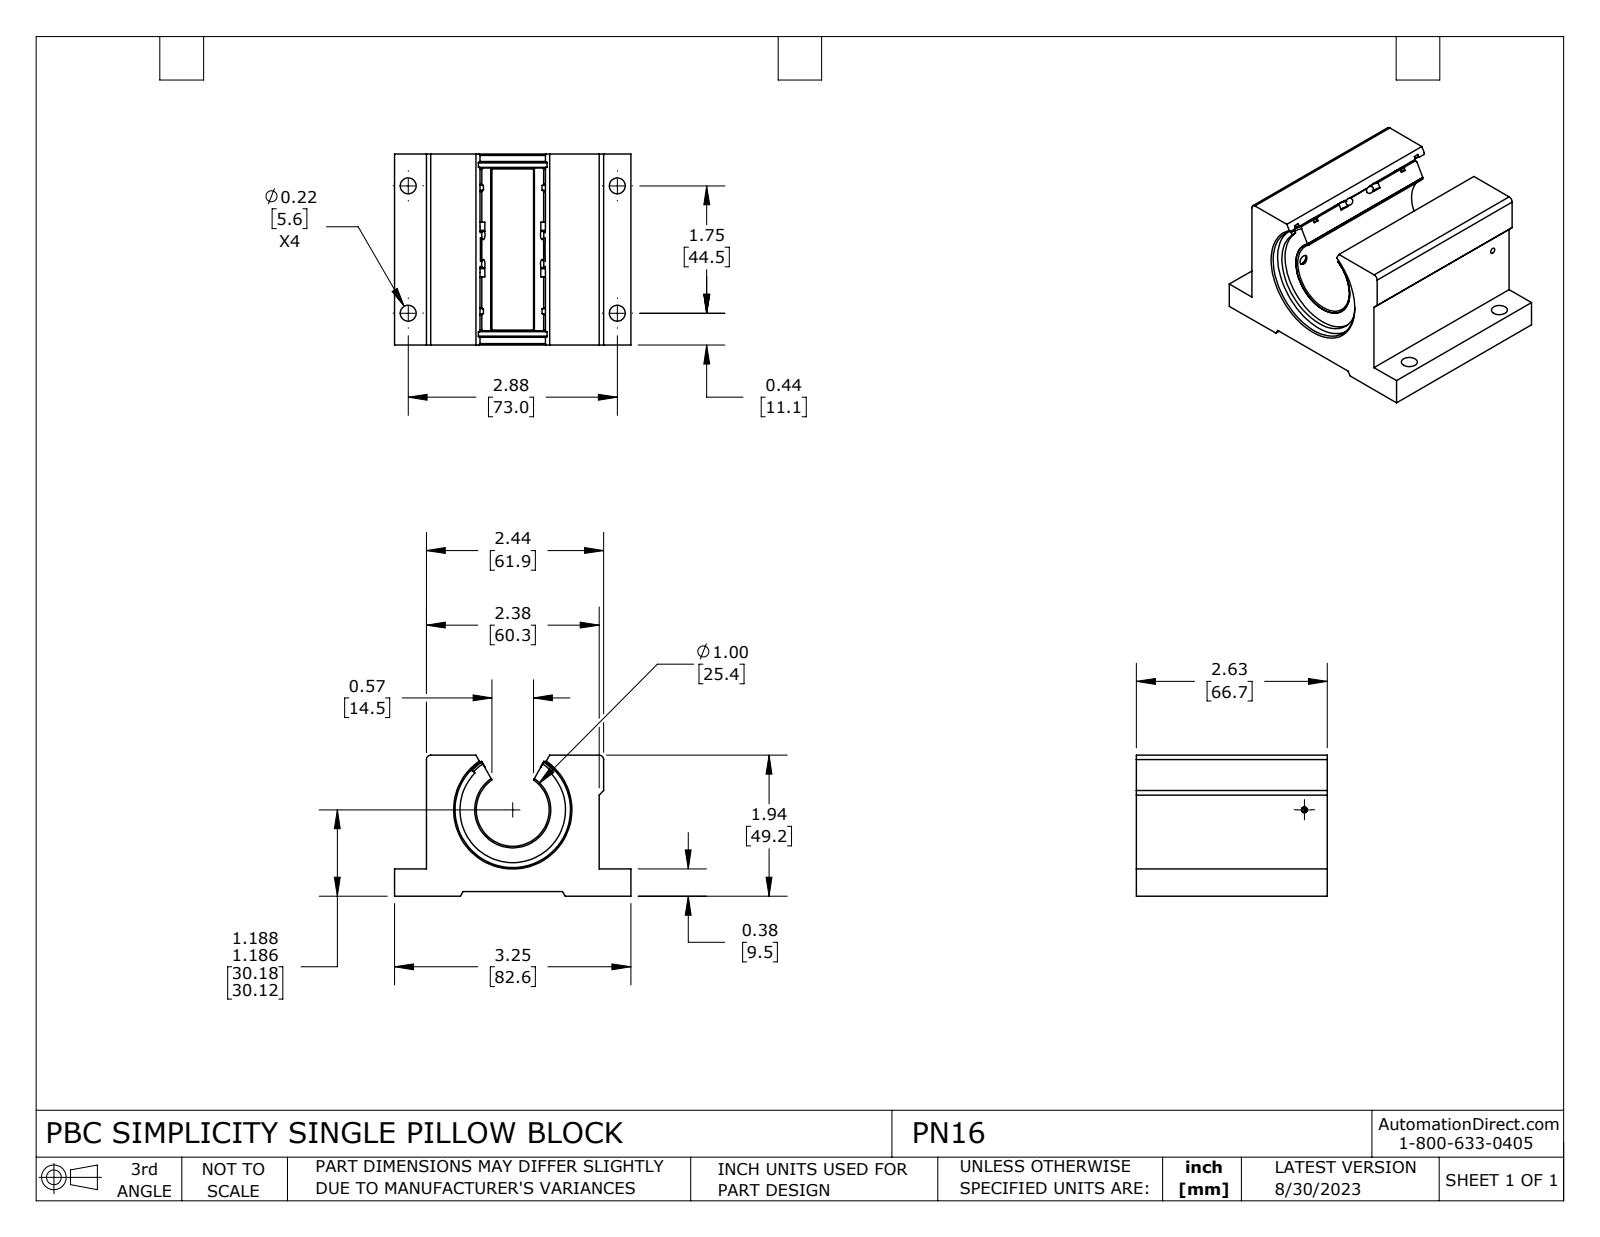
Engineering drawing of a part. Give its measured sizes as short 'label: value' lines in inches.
name: PN16
written by: SolidWorks 2021 (CONFIG_CONTROL_DESIGN)
unit: in
bodies: 8 solids, 206 faces (53 planar, 94 cylindrical, 59 other)
size: 3.25 × 2.625 × 1.938
volume: 9.582 in³; area: 79.88 in²
holes: 4× ⌀0.219, 1× ⌀0.054, 1× ⌀0.079, 1× ⌀0.136, 1× ⌀1.001, 1× ⌀1.045, 1× ⌀1.586, 1× ⌀1.671
bosses: 1× ⌀1.562, 1× ⌀1.471, 1× ⌀1.399, 1× ⌀0.078
rounds: 2× R0.03, 2× R0.06, 2× R0.18, 1× R0.726, 1× R0.846
face distances: 0.065, 1.938, 1.873, 2.625, 2.375, 0.375, 0.31, 1.563, 0.437, 2.812
hole spacings: 1.75, 2.875, 3.366, 1.992
